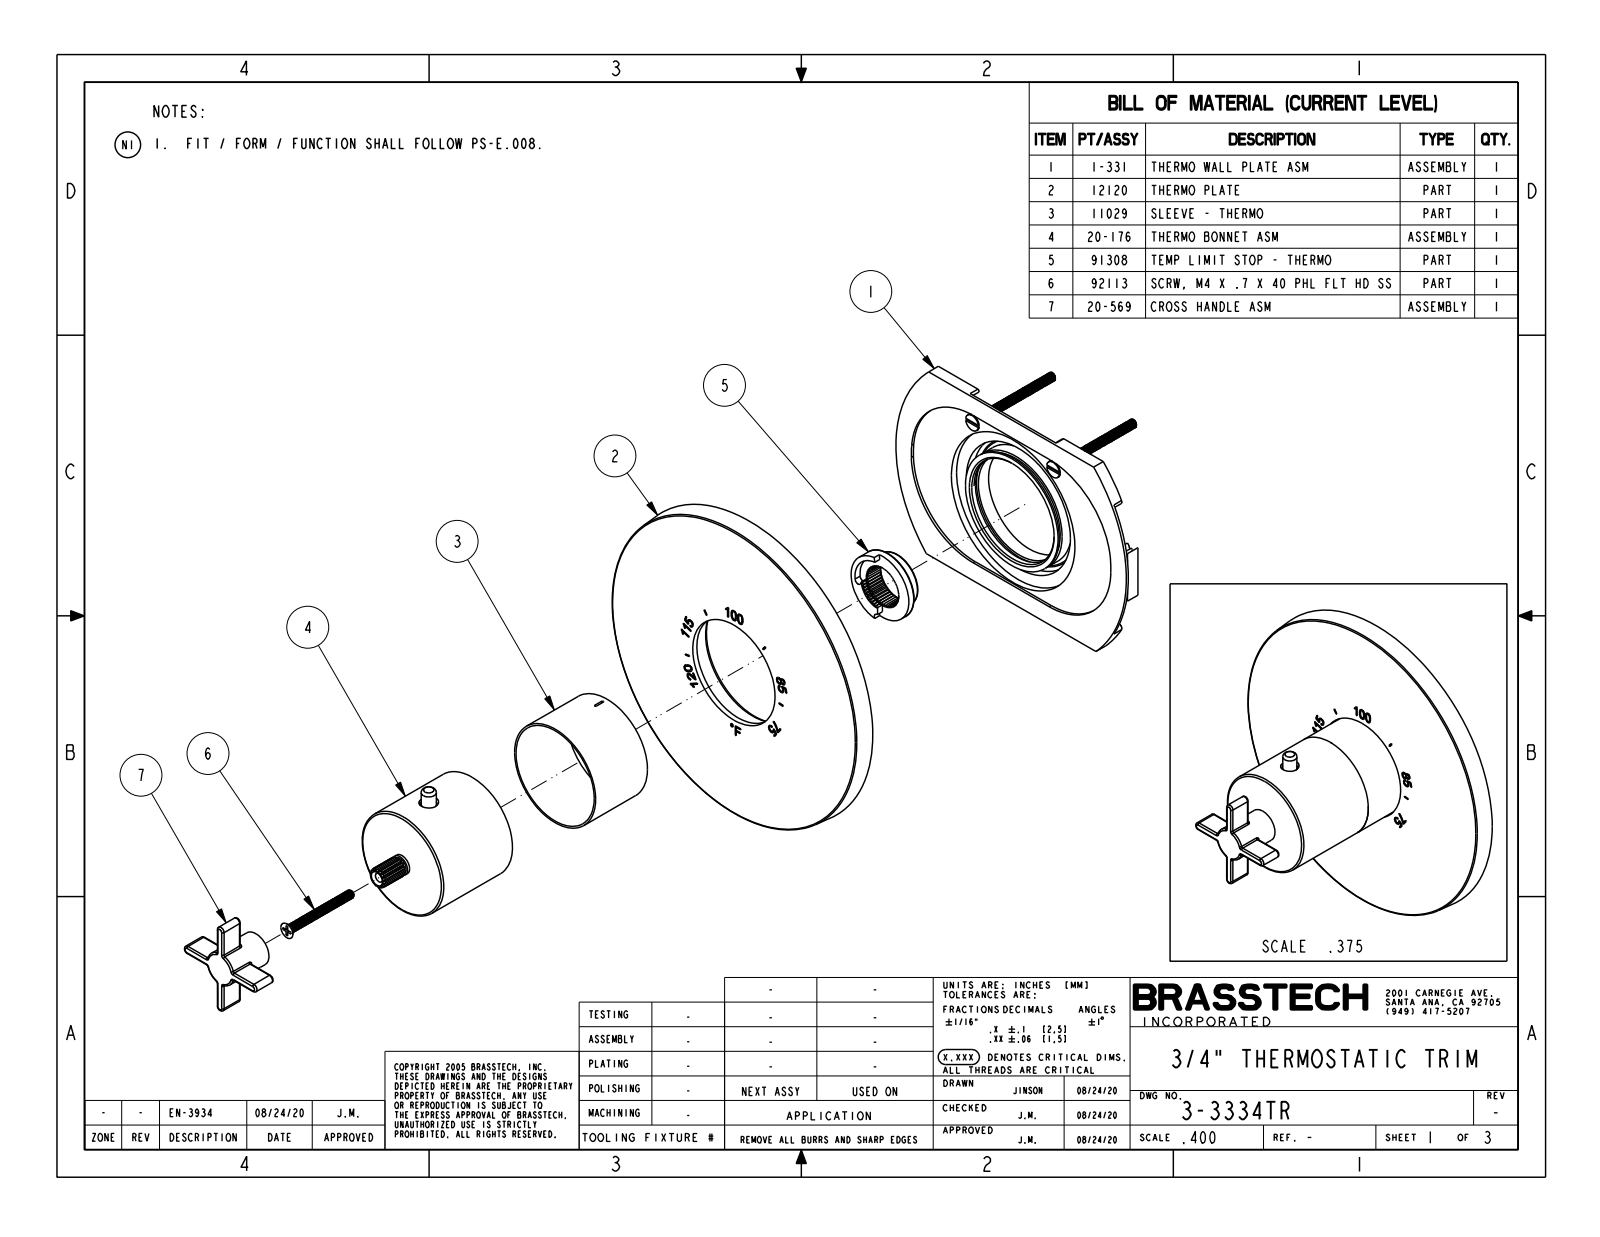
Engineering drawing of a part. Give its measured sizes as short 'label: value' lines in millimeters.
name: 12117; 92075; 91757; H-78_2_FEET (+8 more)
written by: CREO PARAMETRIC BY PTC INC, 2023134 (CONFIG_CONTROL_DESIGN)
unit: mm
bodies: 18 solids, 1651 faces (502 planar, 582 cylindrical, 567 other)
size: 152.4 × 152.2 × 141.9
volume: 128 900 mm³; area: 119 500 mm²
holes: 2× ⌀3.5, 2× ⌀4.8, 1× ⌀1.6, 1× ⌀3, 1× ⌀4.3, 1× ⌀7, 1× ⌀7.1, 1× ⌀8.6, 1× ⌀10.7, 1× ⌀46.5, 1× ⌀48.3, 1× ⌀50.8
bosses: 4× ⌀4.2, 2× ⌀7.9, 2× ⌀3.3, 1× ⌀63.5, 1× ⌀57.2, 1× ⌀54.8, 1× ⌀50, 1× ⌀32.5
rounds: 22× R0.8, 8× R38.1, 6× R1.5, 6× R1.9, 4× R45.2, 2× R2.2, 2× R4.7, 2× R4.8
face distances: 2.3, 1.3, 9.5, 7.2, 2.5, 4.7, 4.8, 6, 3.6, 4.4
hole spacings: 31.3, 43, 16.1, 50
